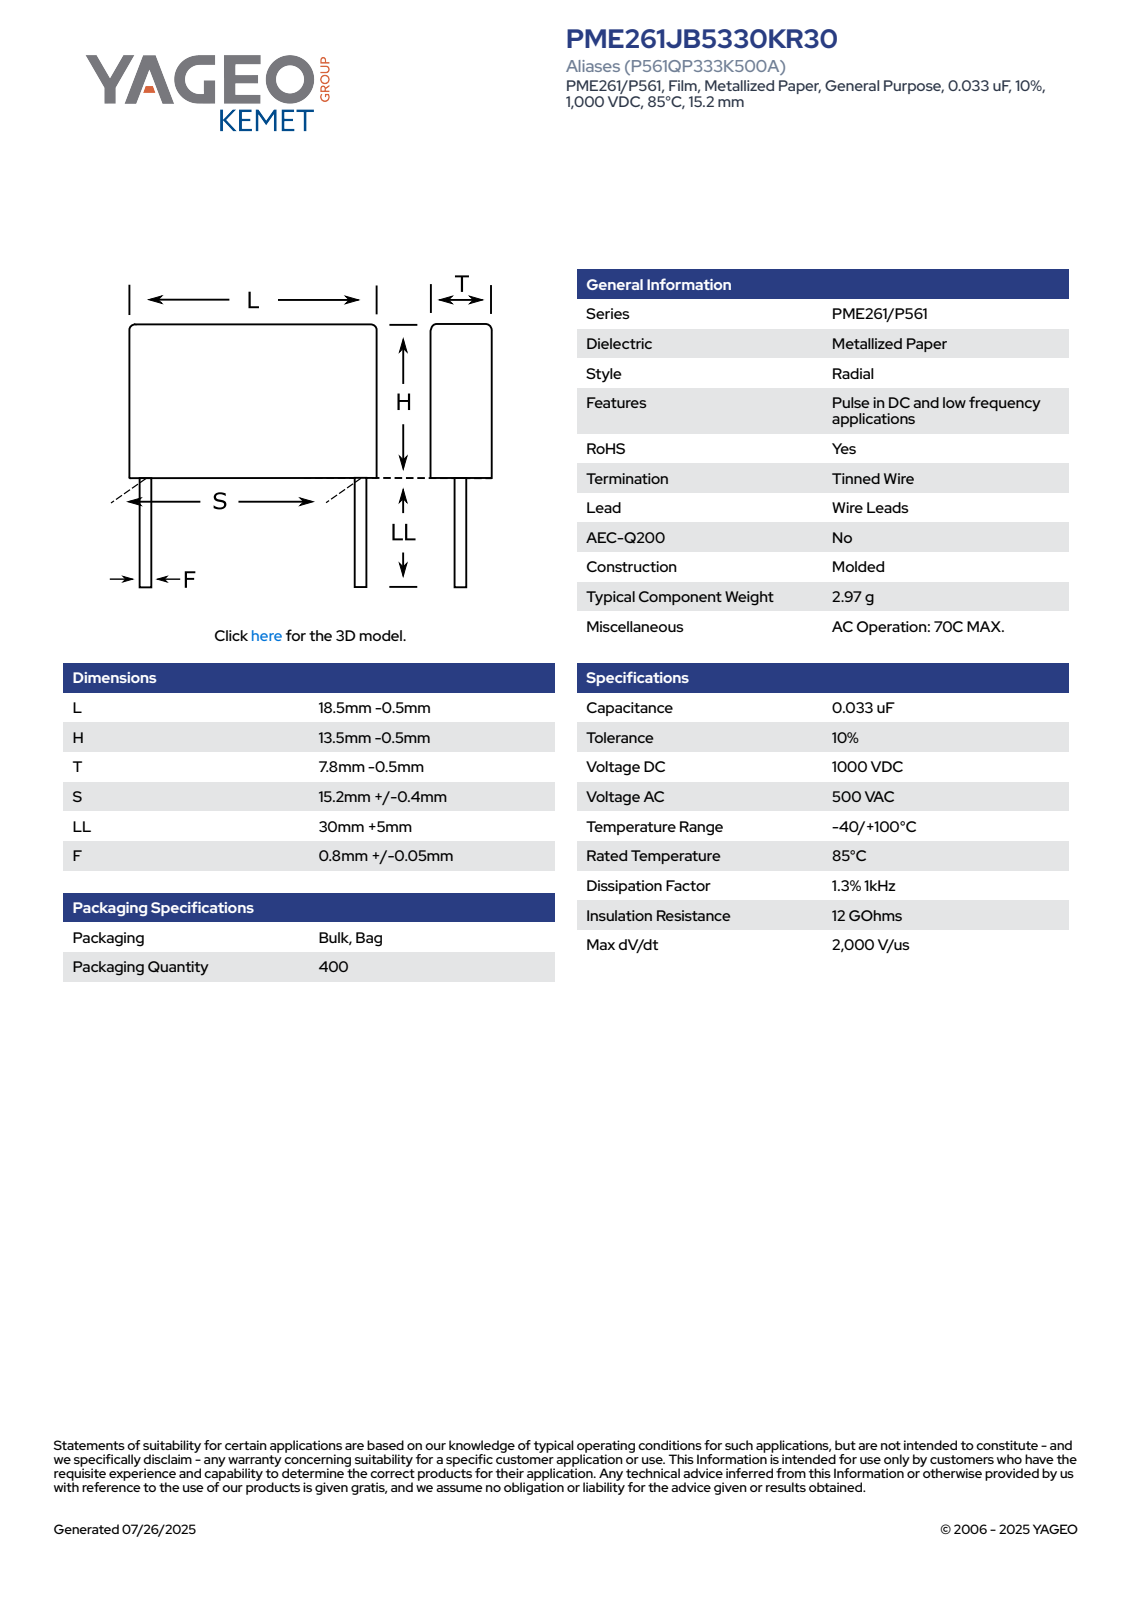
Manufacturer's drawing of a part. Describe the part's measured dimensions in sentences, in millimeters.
The part is named "CFR_MOLDED_18.5X13.5X7.8_L18H13T7.3S15.2LL35F0.85". Its 3-D file was written by "SolidWorks 2014 (AUTOMOTIVE_DESIGN)". It is 4 solids with 73 faces: 65 planar, 8 cylindrical and 0 other. Overall it measures 48 by 18 by 7.3 millimeters. Its volume is 1 745 cubic millimeters and its surface area 1 112 square millimeters. Round bosses or shafts: 2 of diameter 0.85. Partial cylindrical surfaces (rounded edges, fillets, slot ends): 4 of radius 0.5. The main face-to-face distances are 7.3, 13, 18, 35, 48, 42.06, 7.06, 5.94, 40.45, 5.45.
